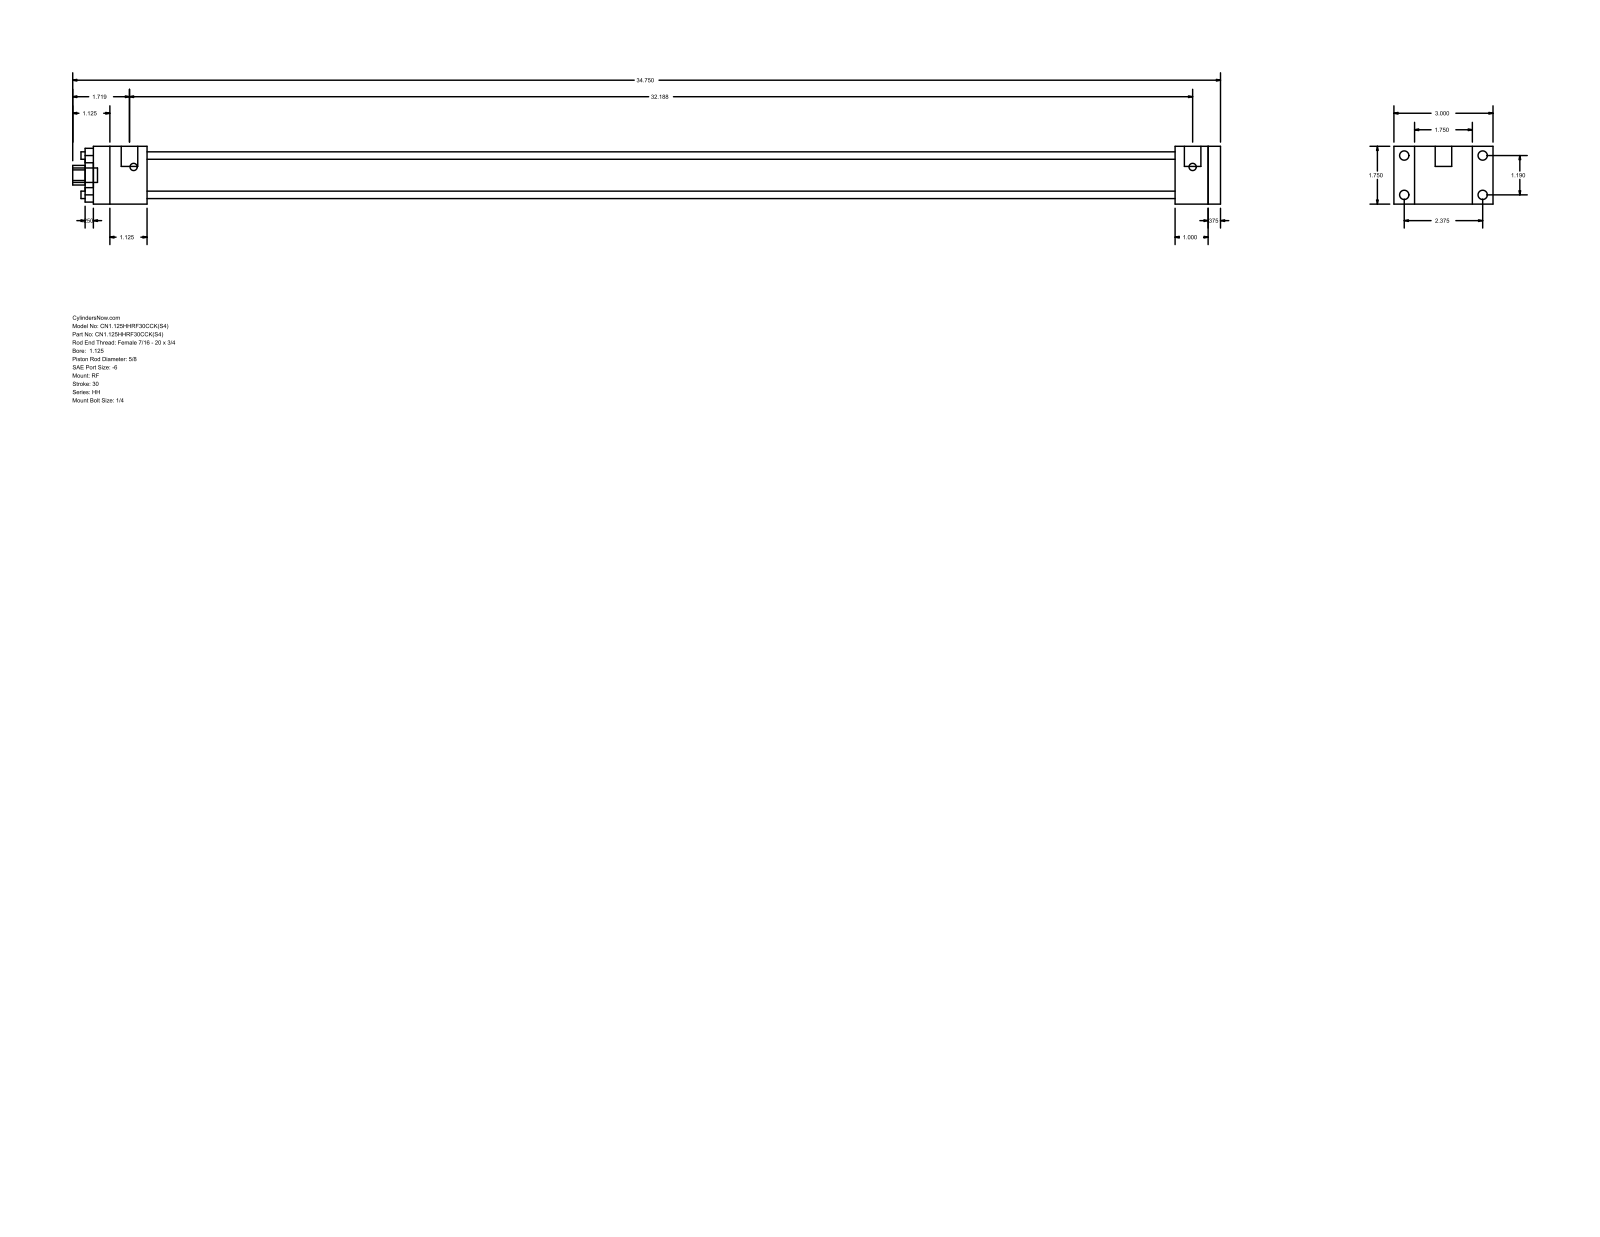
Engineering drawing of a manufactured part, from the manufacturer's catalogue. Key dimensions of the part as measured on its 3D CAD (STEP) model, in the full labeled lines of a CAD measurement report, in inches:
Part name (STEP PRODUCT): HH_RF__0112_0.625
STEP written by: GSSL Pune (CONFIG_CONTROL_DESIGN)
Units: inches
Bodies: 0 solids, 92 faces (64 planar, 28 cylindrical, 0 other)
Overall size (bounding box): 34.75 × 3 × 1.75
Round holes (diameter × count): ⌀0.225 ×4, ⌀0.625 ×1, ⌀1.125 ×1, ⌀1.375 ×1
Round bosses / shafts (diameter × count): ⌀0.281 ×4, ⌀0.219 ×4, ⌀0.5 ×2, ⌀0.437 ×1
Partial cylindrical surfaces — rounded edges, fillets, slot ends (radius × count): R0.297 ×1
Main face-to-face distances: 1.75, 0.375, 34.125, 0.625, 32.125, 32.5, 31.125, 1, 1.375, 1.625
Hole centre spacings: 0.841, 1.19, 1.683
